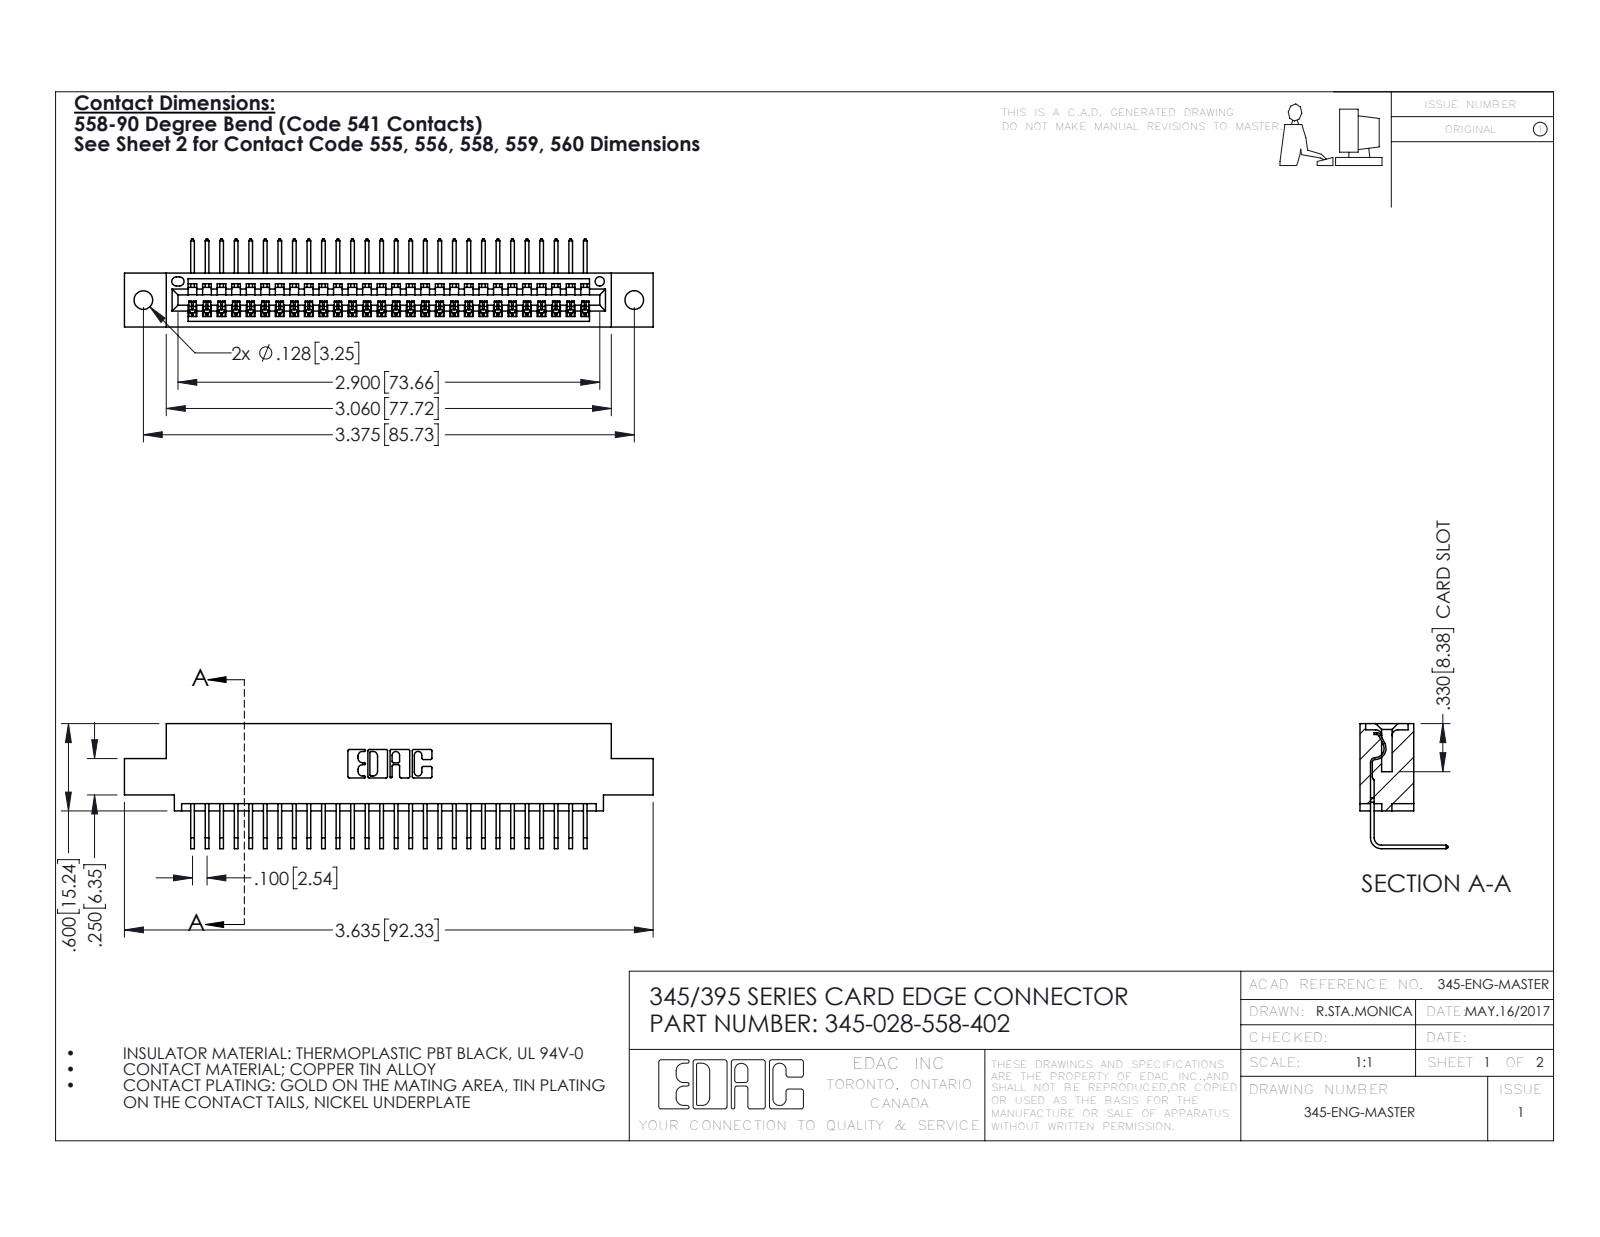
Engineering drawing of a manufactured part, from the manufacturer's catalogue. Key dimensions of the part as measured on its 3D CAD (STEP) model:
Part name (STEP PRODUCT): 345-028-558-402; 345 Part_0.110 Offset - 0.128 Dia; 345-292-001_558 Tail - 2
STEP written by: SolidWorks 2016 (CONFIG_CONTROL_DESIGN)
Units: inches
Bodies: 29 solids, 1810 faces (1260 planar, 550 cylindrical, 0 other)
Overall size (bounding box): 3.635 × 0.859 × 0.605
Volume: 0.527 in³ · Surface area: 18.05 in²
Round holes (diameter × count): ⌀0.128 ×2, ⌀0.064 ×1
Partial cylindrical surfaces — rounded edges, fillets, slot ends (radius × count): R0.006 ×56, R0.01 ×22, R0.007 ×6, R0.031 ×6, R0.026 ×3, R0.031 ×2, R0.04 ×2, R0.014 ×1
Main face-to-face distances: 0.072, 0.298, 0.37, 0.2, 0.098, 0.272, 0.025, 0.225, 0.149, 0.072
Hole centre spacings: 0.27, 3.14, 3.375
